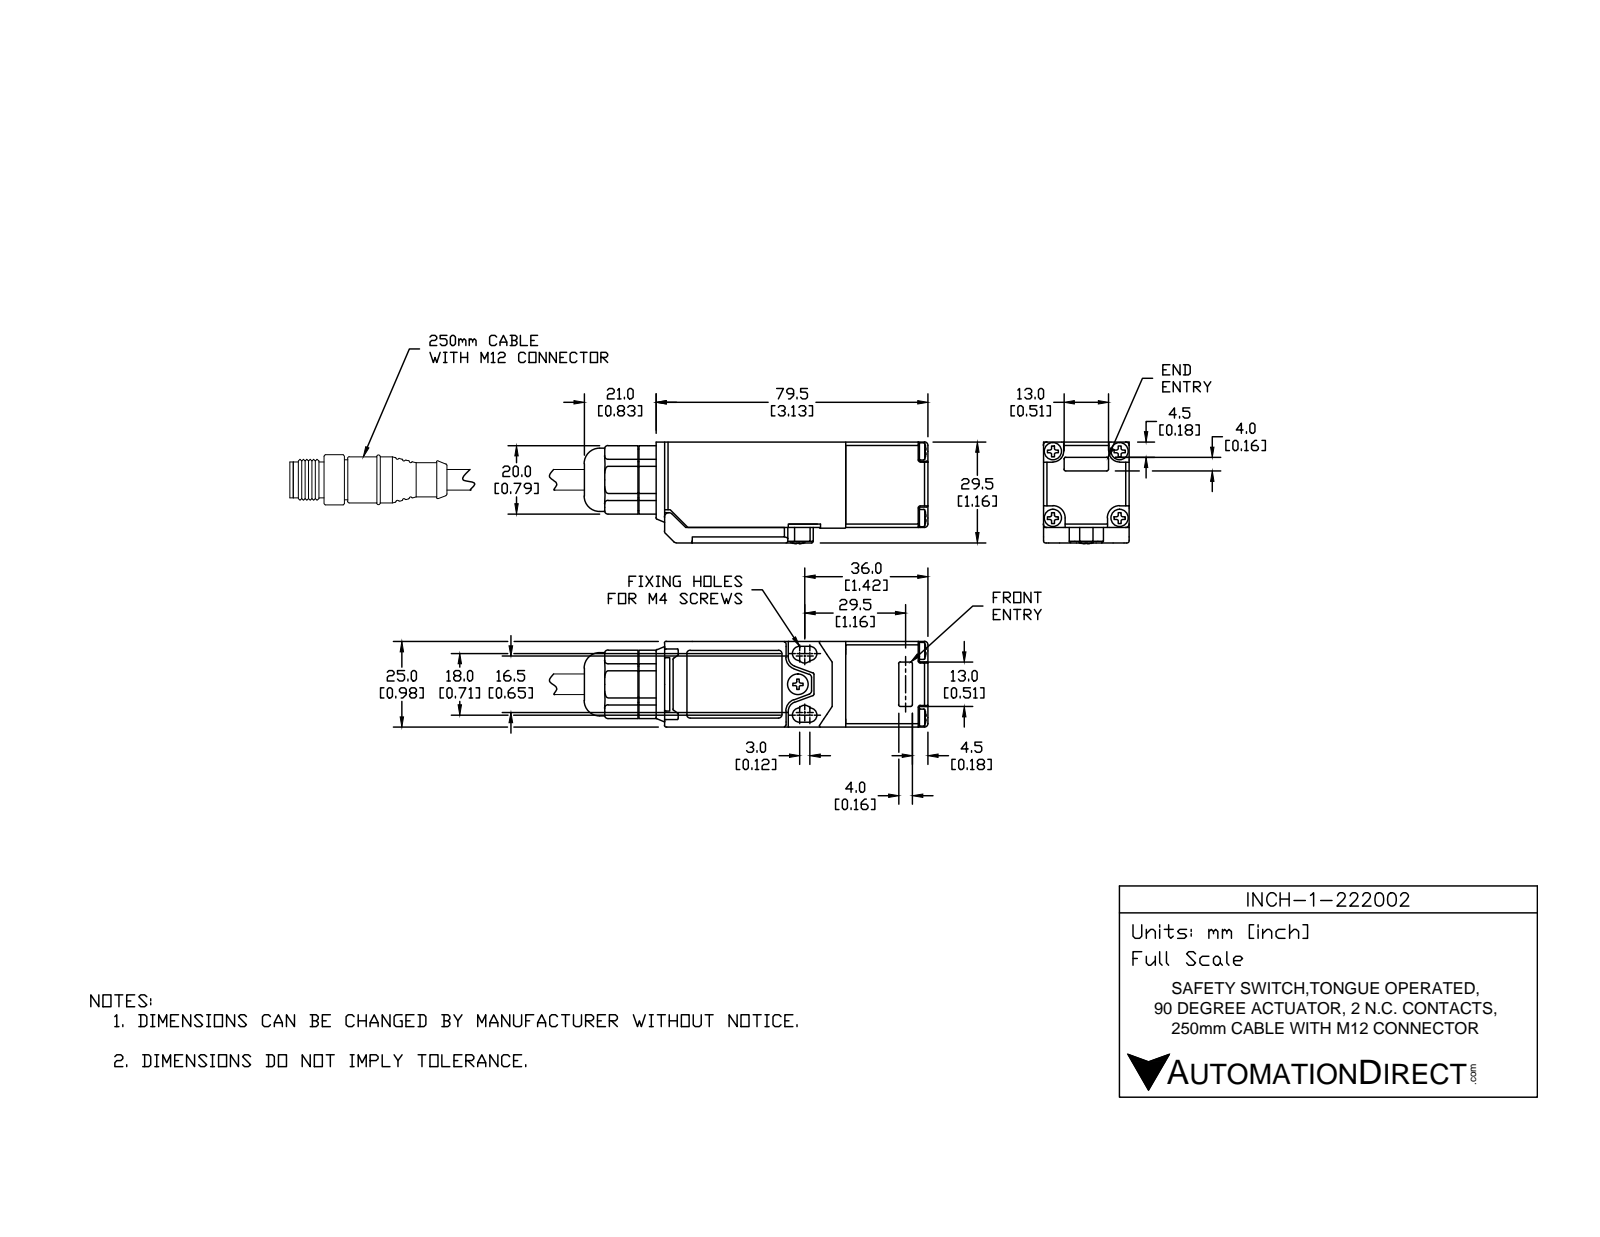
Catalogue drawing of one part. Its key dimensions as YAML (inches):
part_name: "INCH-1-222002"
step_written_by: "SolidWorks 2014 (AUTOMOTIVE_DESIGN)"
units: inches
bodies: {solids: 14, faces: 1863, planar: 738, cylindrical: 677, other: 448}
overall_size: [3.169, 1.172, 0.984]
volume: 1.453
surface_area: 40.72
round_holes:
  - {diameter: 0.126, count: 5}
  - {diameter: 0.094, count: 4}
  - {diameter: 0.059, count: 2}
  - {diameter: 0.063, count: 2}
  - {diameter: 0.071, count: 2}
  - {diameter: 0.087, count: 2}
  - {diameter: 0.142, count: 2}
  - {diameter: 0.055, count: 1}
  - {diameter: 0.098, count: 1}
  - {diameter: 0.102, count: 1}
  - {diameter: 0.197, count: 1}
  - {diameter: 0.217, count: 1}
round_bosses_or_shafts:
  - {diameter: 0.102, count: 5}
  - {diameter: 0.197, count: 4}
  - {diameter: 0.079, count: 4}
  - {diameter: 0.138, count: 2}
  - {diameter: 0.74, count: 1}
  - {diameter: 0.531, count: 1}
  - {diameter: 0.213, count: 1}
  - {diameter: 0.118, count: 1}
partial_cylinders:
  - {radius: 0.02, count: 236}
  - {radius: 0.012, count: 85}
  - {radius: 0.004, count: 24}
  - {radius: 0.039, count: 24}
  - {radius: 0.031, count: 10}
  - {radius: 0.083, count: 6}
  - {radius: 0.11, count: 6}
  - {radius: 0.008, count: 4}
face_to_face_distances: [0.984, 0.079, 0.039, 0.906, 0.02, 0.874, 0.024, 0.945, 0.929, 0.913]
hole_center_spacings: [0.543, 0.768, 0.171, 0.187, 0.423, 0.426, 0.45, 0.581]
